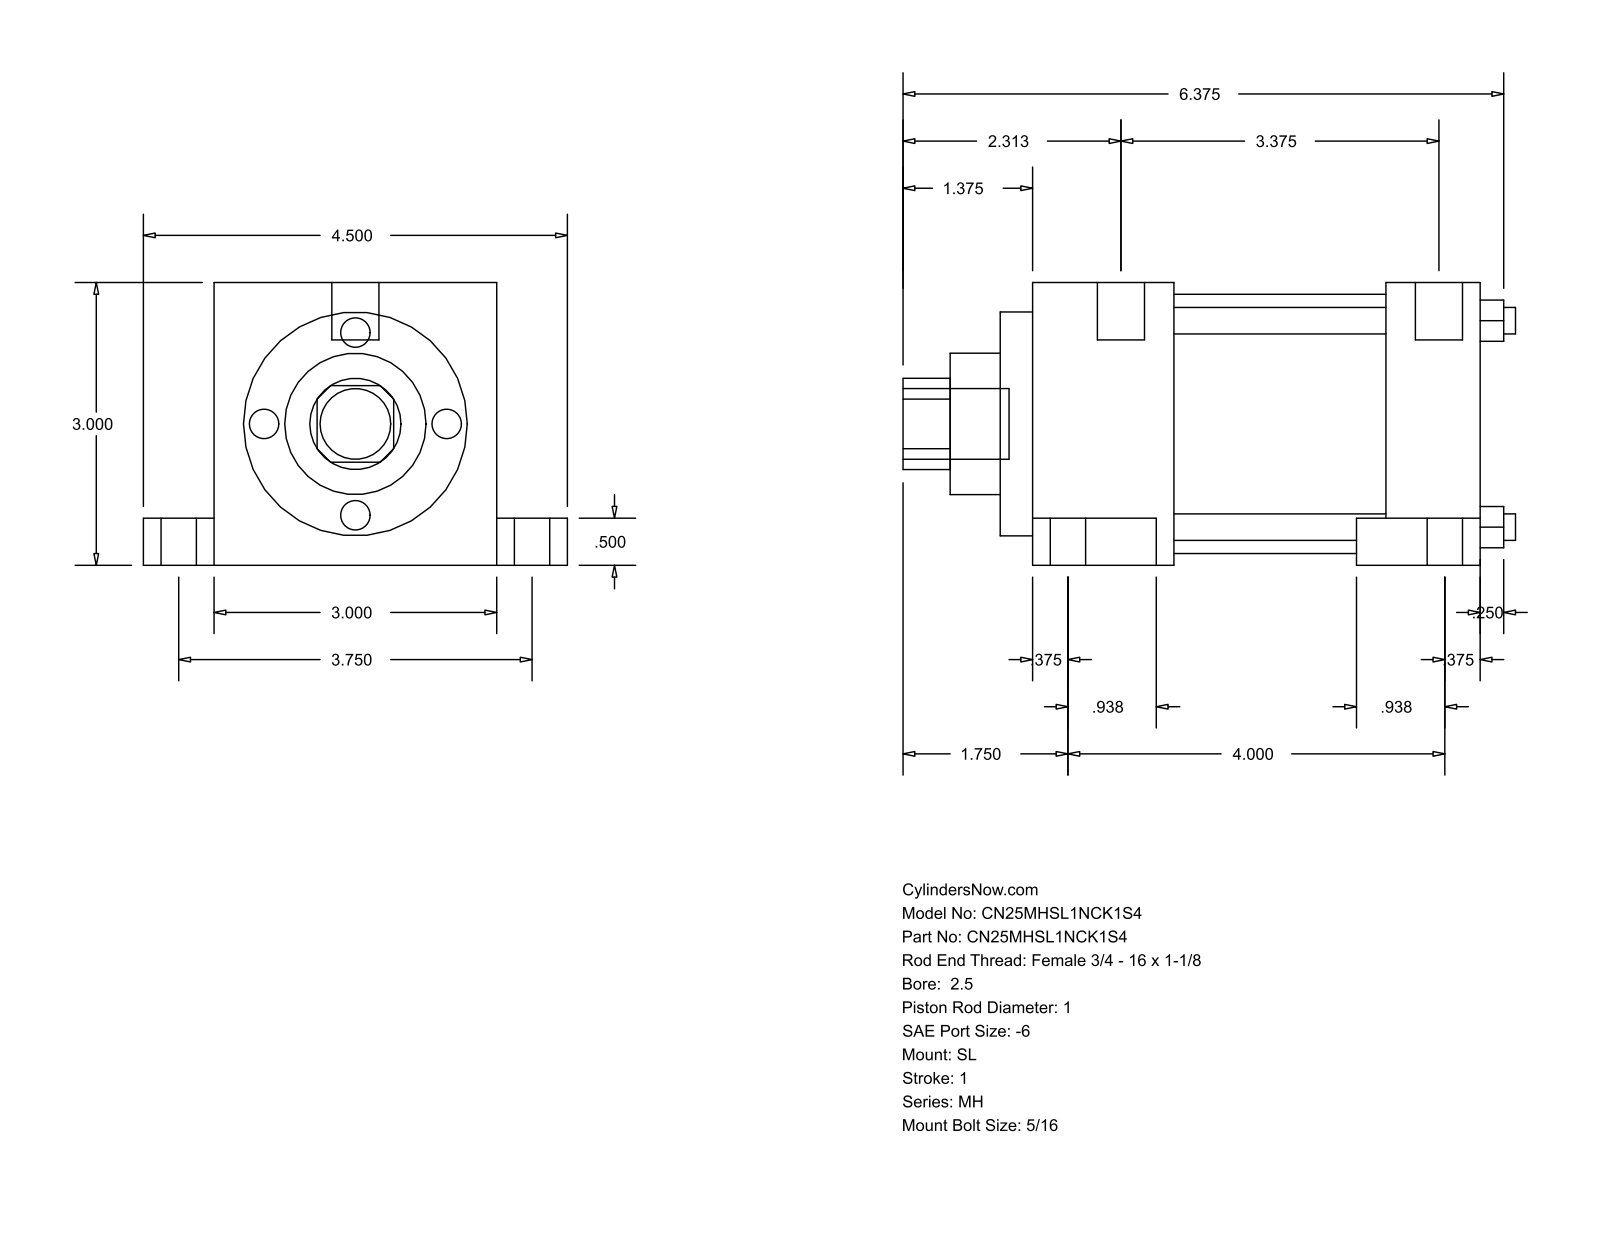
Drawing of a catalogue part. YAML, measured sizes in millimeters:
part_name: "MH_SL__0250_1"
step_written_by: "GSSL Pune (CONFIG_CONTROL_DESIGN)"
units: millimeters
bodies: {solids: 0, faces: 86, planar: 61, cylindrical: 25, other: 0}
overall_size: [165.1, 114.3, 76.2]
round_holes:
  - {diameter: 7.14, count: 4}
  - {diameter: 25.4, count: 1}
  - {diameter: 38.1, count: 1}
  - {diameter: 60.33, count: 1}
  - {diameter: 69.85, count: 1}
round_bosses_or_shafts:
  - {diameter: 15.88, count: 2}
  - {diameter: 9.53, count: 2}
  - {diameter: 5.56, count: 2}
  - {diameter: 19.05, count: 1}
  - {diameter: 12.7, count: 1}
partial_cylinders:
  - {radius: 12.29, count: 1}
face_to_face_distances: [76.2, 25.39, 103.99, 129.38, 12.7, 63.5, 19.05, 95.25, 13.49, 117.48]
hole_center_spacings: [39.33, 55.62, 78.66]
